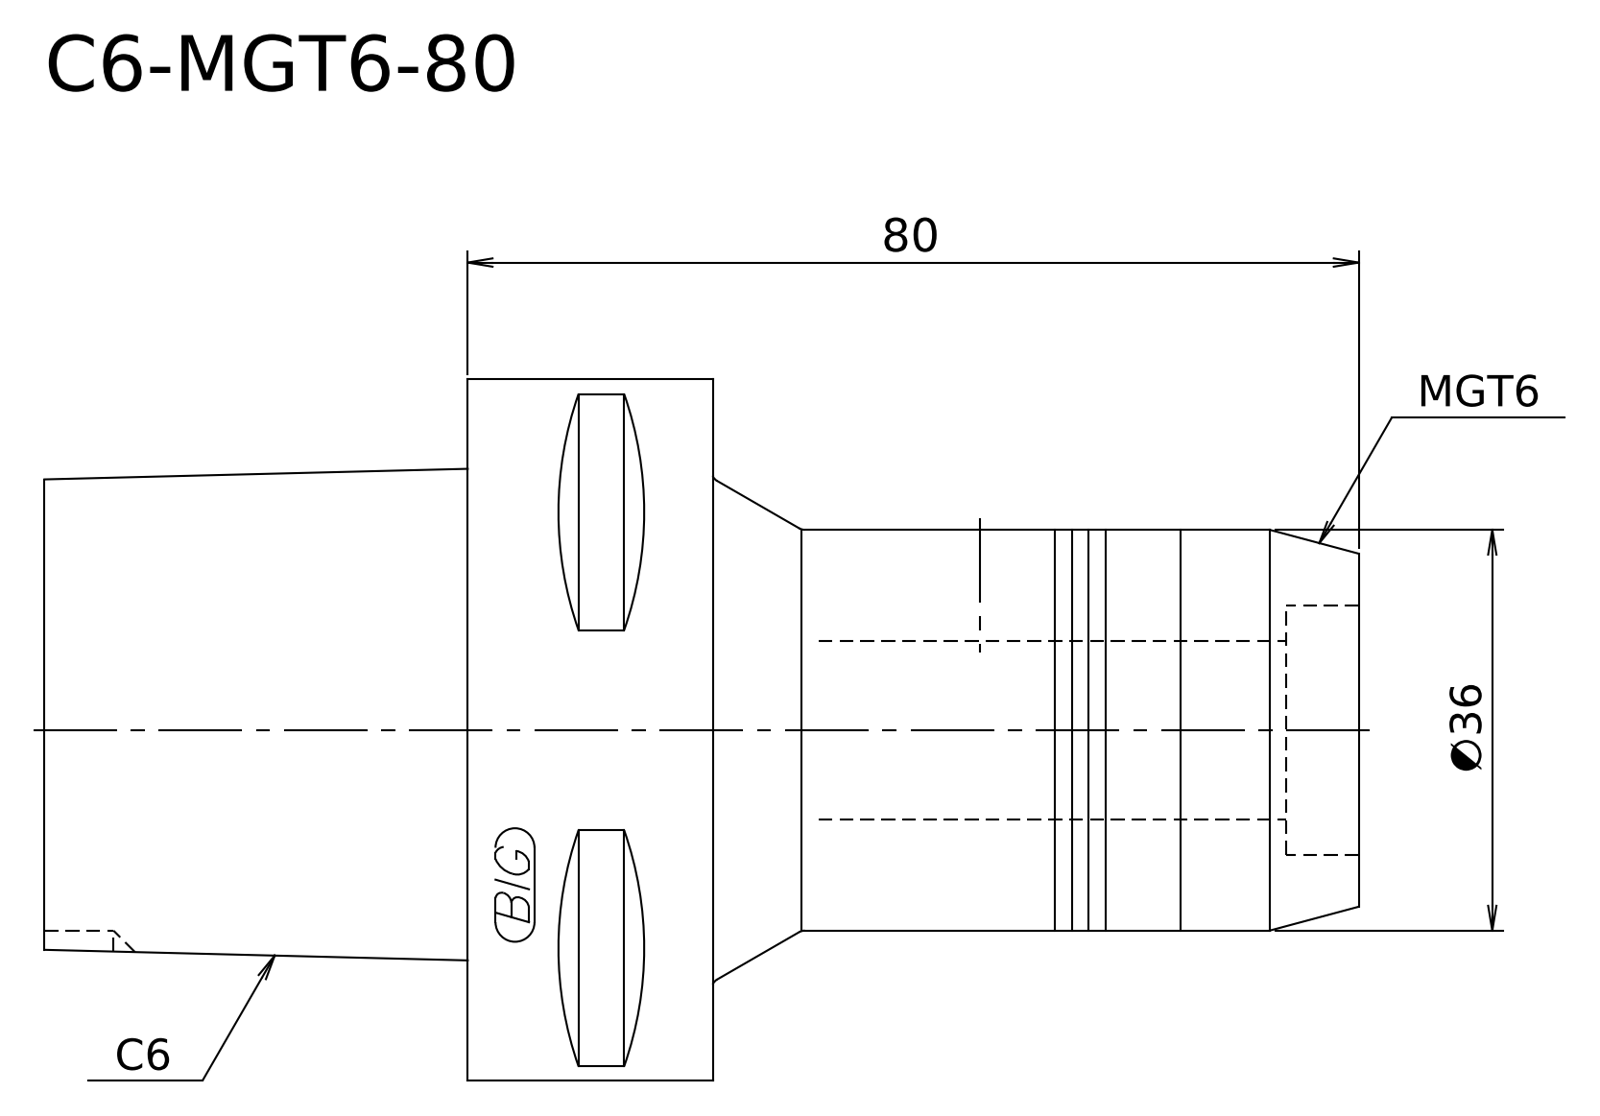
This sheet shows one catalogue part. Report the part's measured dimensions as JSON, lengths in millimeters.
{"step_written_by": "Kubotek KeyCreator V8.5.1 (14335) (CONFIG_CONTROL_DESIGN)", "units": "millimeters", "bodies": {"solids": 1, "faces": 11, "planar": 4, "cylindrical": 2, "other": 5}, "overall_size": [118, 62.98, 62.98], "volume_mm3": 183698, "surface_area_mm2": 21606, "round_bosses_or_shafts": [[62.98, 1], [36, 1]], "face_to_face_distances": [22, 60, 38, 58, 80, 118]}
